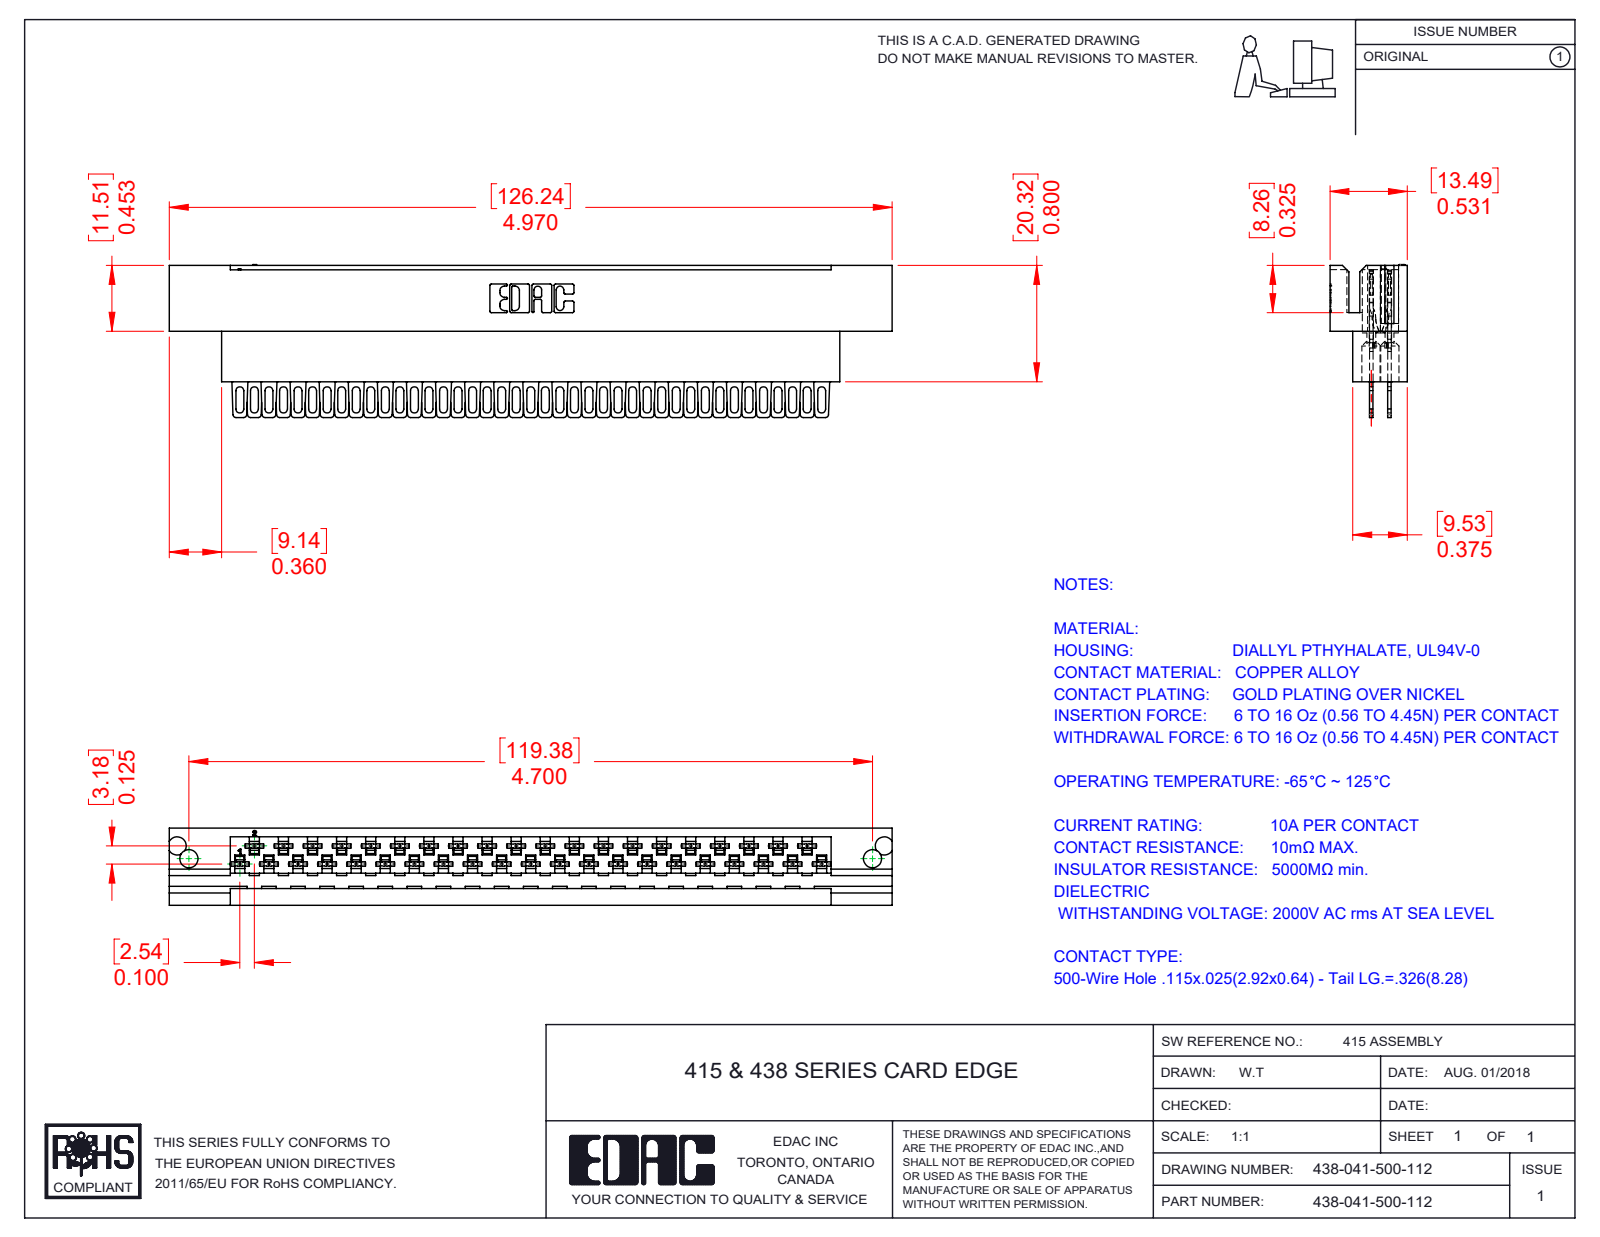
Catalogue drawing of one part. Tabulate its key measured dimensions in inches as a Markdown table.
| quantity | value |
| --- | --- |
| part name | 516-290-001_500; 438-041-500-112; 438-210-001_438-210-041-112 |
| STEP written by | SolidWorks 2016 (CONFIG_CONTROL_DESIGN) |
| units | inches |
| bodies | 42 solids, 4330 faces (2700 planar, 1239 cylindrical, 391 other) |
| overall size | 4.97 × 1.05 × 0.531 |
| volume | 1.285 in³ |
| surface area | 41.66 in² |
| round holes (diameter × count) | 0.05 × 41, 0.13 × 41, 0.125 × 1, 0.125 × 1 |
| partial cylindrical surfaces (radius × count) | 0.012 × 164, 0.022 × 164, 0.007 × 82, 0.008 × 82, 0.016 × 82, 0.02 × 82, 0.027 × 82, 0.08 × 82 |
| main face-to-face distances | 0.125, 0.024, 0.074, 0.05, 0.295, 0.115, 0.156, 0.531, 0.26, 0.271 |
| hole center spacings | 0.2, 0.4, 0.6, 0.8, 1, 1.2, 1.4, 0.1 |
